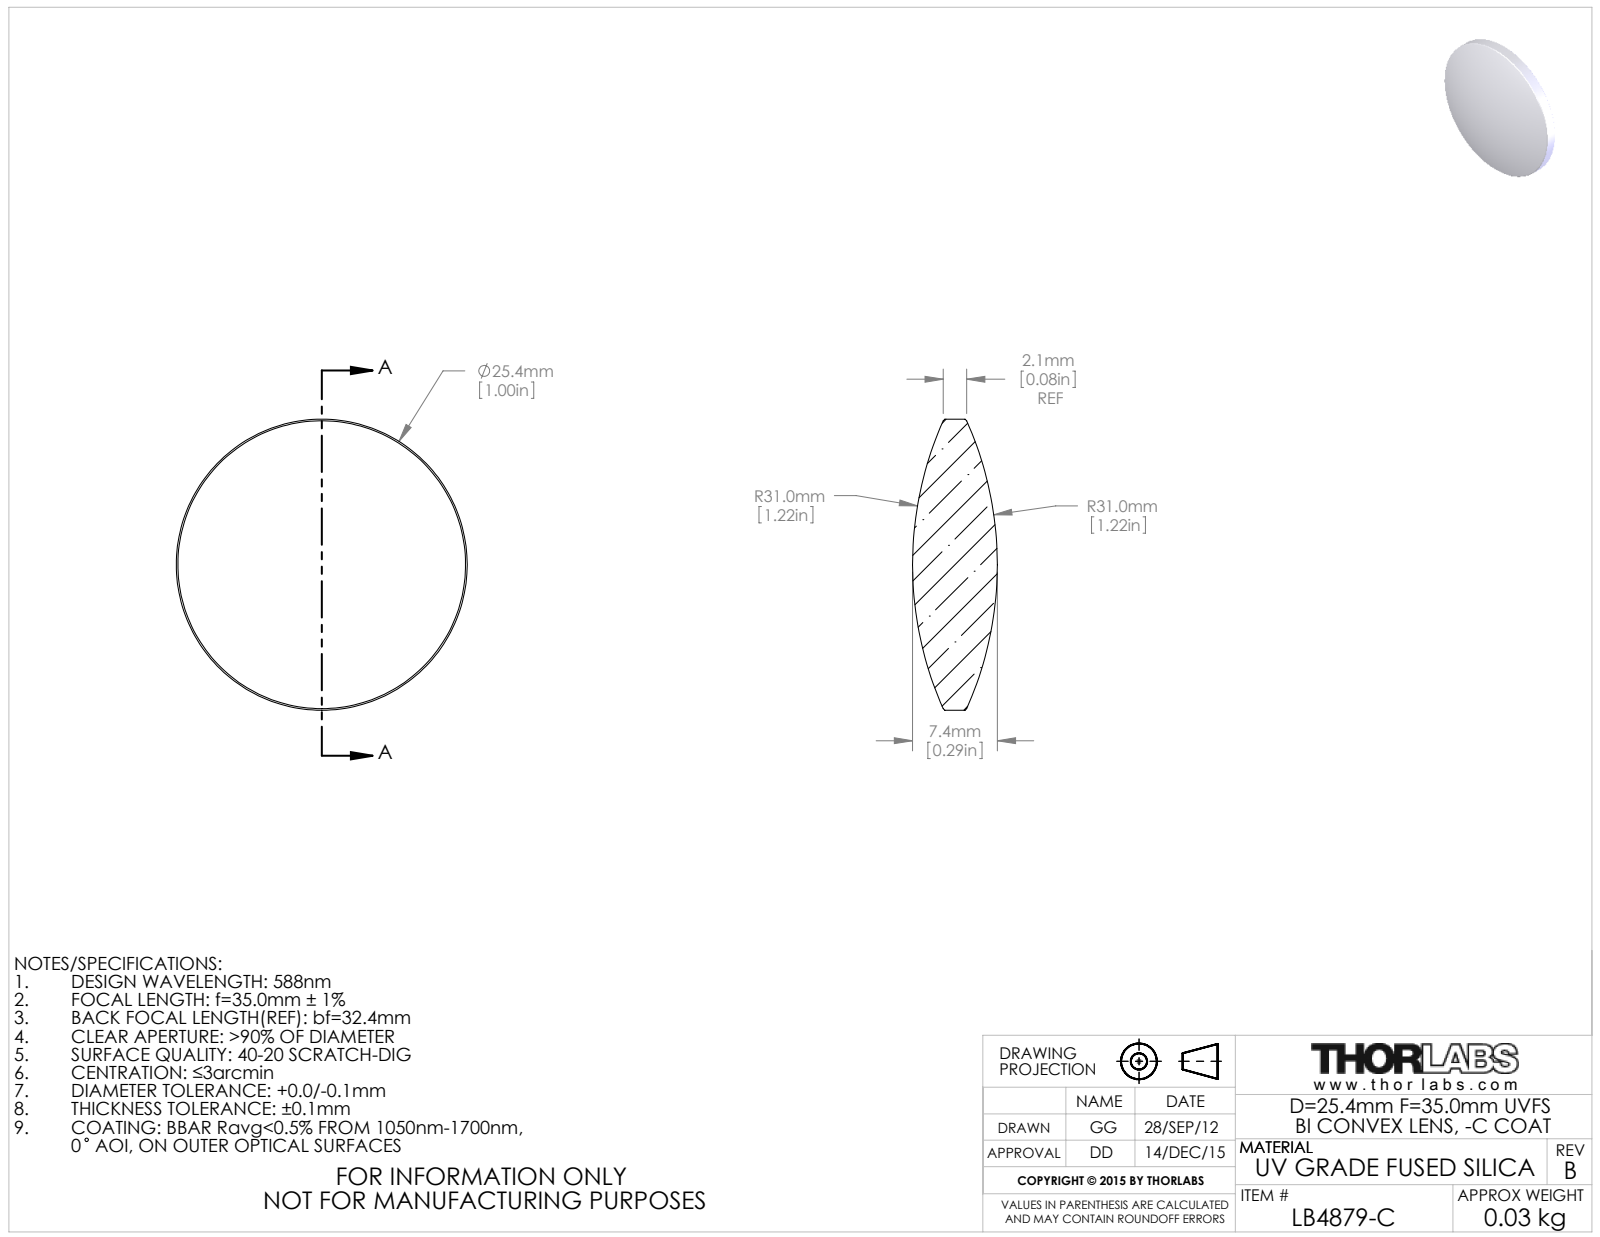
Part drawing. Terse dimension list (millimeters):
name: 25016-E0W
written by: SolidWorks 2011 (CONFIG_CONTROL_DESIGN)
unit: mm
bodies: 1 solid, 10 faces (0 planar, 2 cylindrical, 8 other)
size: 25.4 × 25.4 × 7.4
volume: 2 381 mm³; area: 1 209 mm²
bosses: 1× ⌀25.4
